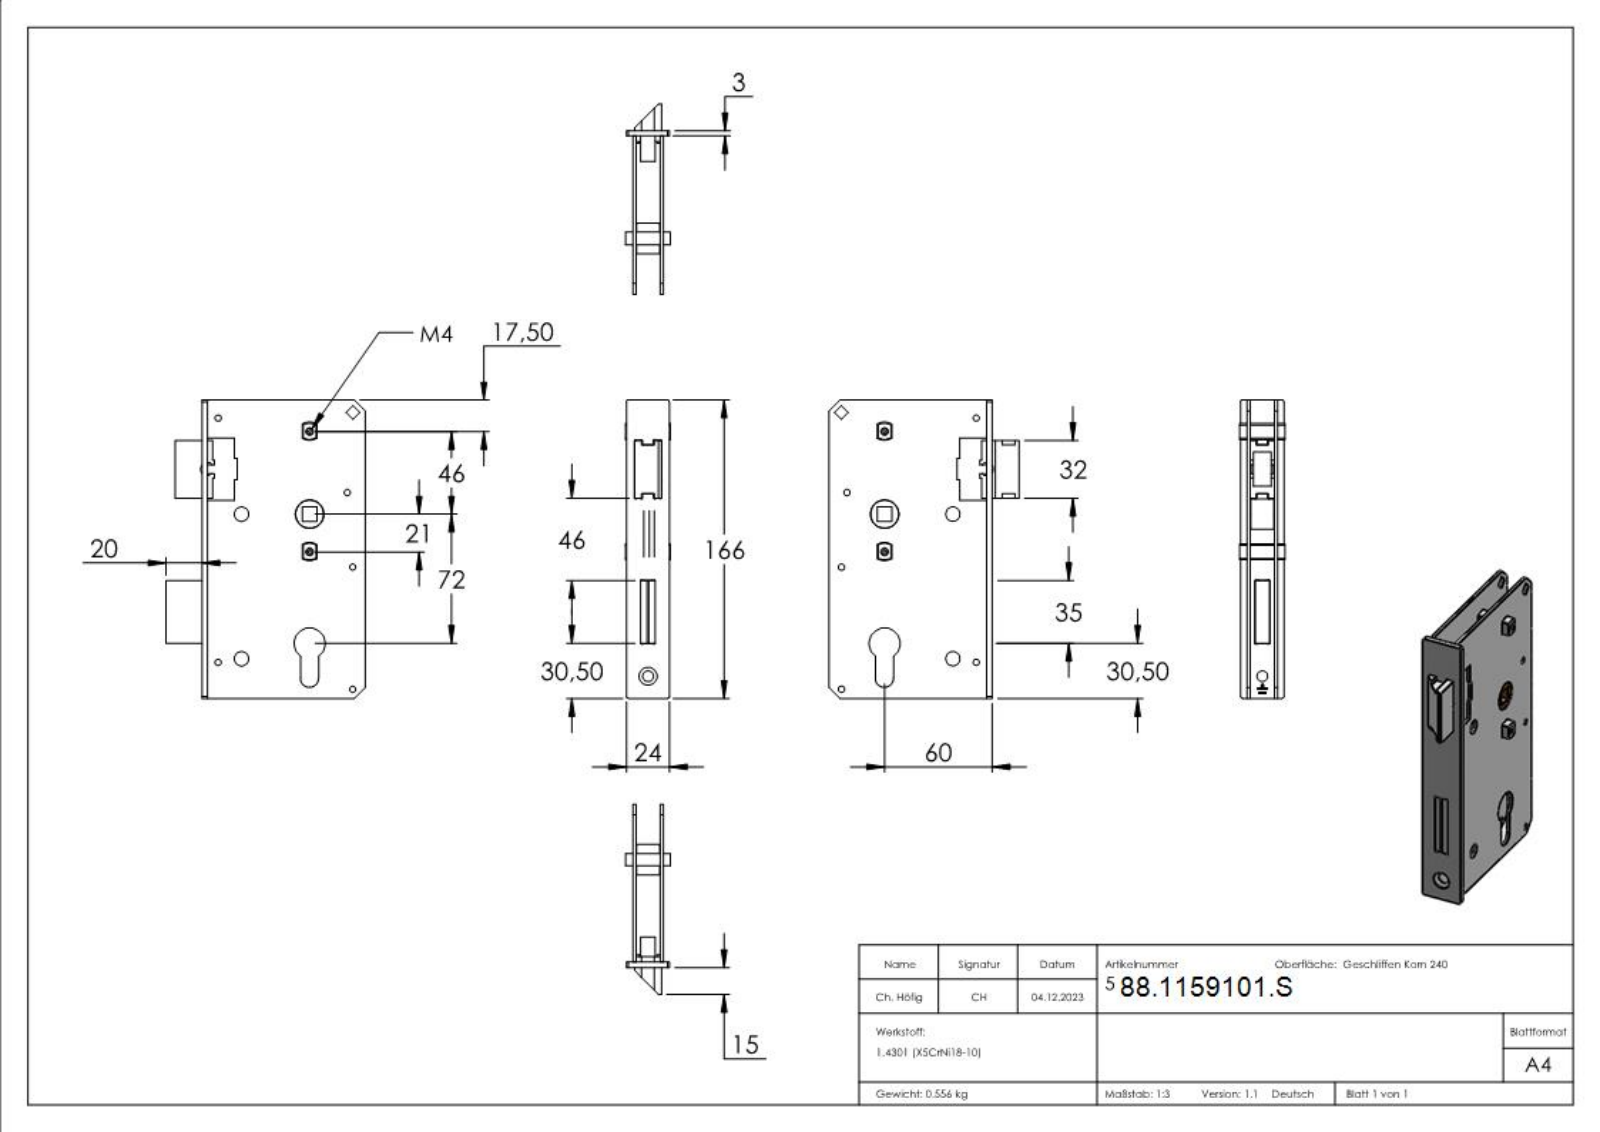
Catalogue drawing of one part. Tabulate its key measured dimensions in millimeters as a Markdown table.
| quantity | value |
| --- | --- |
| part name | Schlosskasten Teil4 Konfig_59XXX-240 Teil4; 59101-S; Schlosskasten Teil3 Konfig_59XXX-240 Teil3; Schlosskasten Teil2 Konfig_59101-240 Teil2 (+1 more) |
| STEP written by | SolidWorks 2018 (CONFIG_CONTROL_DESIGN) |
| units | millimeters |
| bodies | 8 solids, 446 faces (253 planar, 71 cylindrical, 122 other) |
| overall size | 166 × 106 × 25 |
| volume | 70 178 mm³ |
| surface area | 72 475 mm² |
| round holes (diameter × count) | 3.5 × 5, 3.3 × 2, 8 × 2, 6 × 1, 10 × 1, 16 × 1, 17.3 × 1 |
| round bosses / shafts (diameter × count) | 17 × 1, 15.5 × 1 |
| partial cylindrical surfaces (radius × count) | 0.3 × 8, 0.6 × 8, 0.5 × 4, 1 × 4, 4.39 × 4, 7.5 × 4, 8 × 4, 2.4 × 1 |
| main face-to-face distances | 15.25, 1.75, 17, 13.5, 3, 20.5, 3.5, 5.25, 18.75, 3.4 |
| hole center spacings | 13.15, 21, 24.19, 25.46, 35.02, 38, 38.03, 38.94 |
